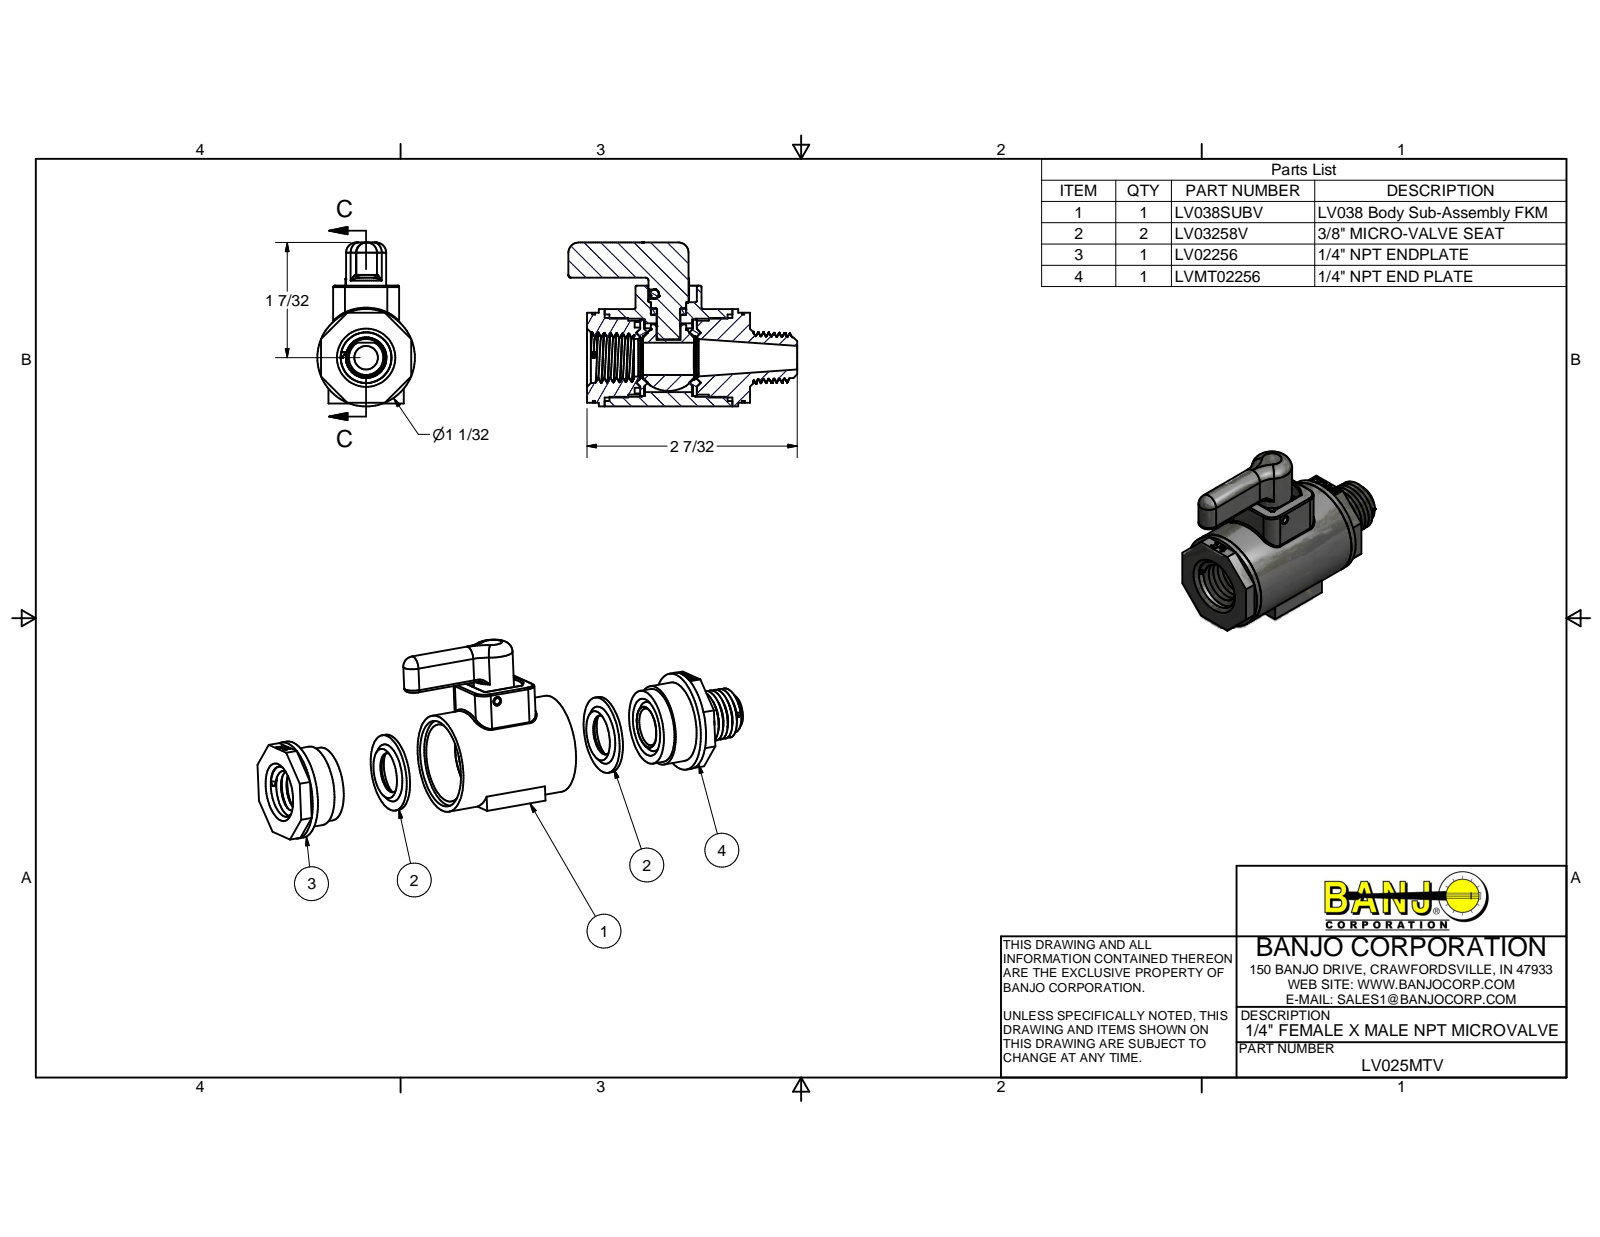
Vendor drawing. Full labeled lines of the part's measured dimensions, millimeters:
Part name (STEP PRODUCT): LV025MTV; LV038SUBV; LV03254A; AQ010V (+6 more)
STEP written by: Autodesk Inventor 2012 (AUTOMOTIVE_DESIGN)
Units: millimetres
Bodies: 9 solids, 667 faces (312 planar, 106 cylindrical, 249 other)
Overall size (bounding box): 61.6 × 44.3 × 26.3
Volume: 24 170 mm³ · Surface area: 17 500 mm²
Round holes (diameter × count): ⌀1.5 ×4, ⌀2.4 ×1, ⌀6.4 ×1, ⌀9.3 ×1, ⌀9.4 ×1, ⌀9.6 ×1, ⌀10.2 ×1, ⌀10.7 ×1, ⌀18.5 ×1, ⌀20.7 ×1, ⌀21.1 ×1, ⌀23.4 ×1
Round bosses / shafts (diameter × count): ⌀26.3 ×1, ⌀21.5 ×1, ⌀20.6 ×1, ⌀19.9 ×1, ⌀10.8 ×1, ⌀9.5 ×1, ⌀9.4 ×1, ⌀6.4 ×1
Partial cylindrical surfaces — rounded edges, fillets, slot ends (radius × count): R0.3 ×16, R0.4 ×14, R3.2 ×4, R0.8 ×2, R1.3 ×2, R2.8 ×2, R6.4 ×2, R1.2 ×1
Main face-to-face distances: 24.8, 4.8, 39.2, 14.4, 29.6, 9.6, 1.3, 8.3, 43.9, 34.4
Hole centre spacings: 8.9, 12.5, 17.8
